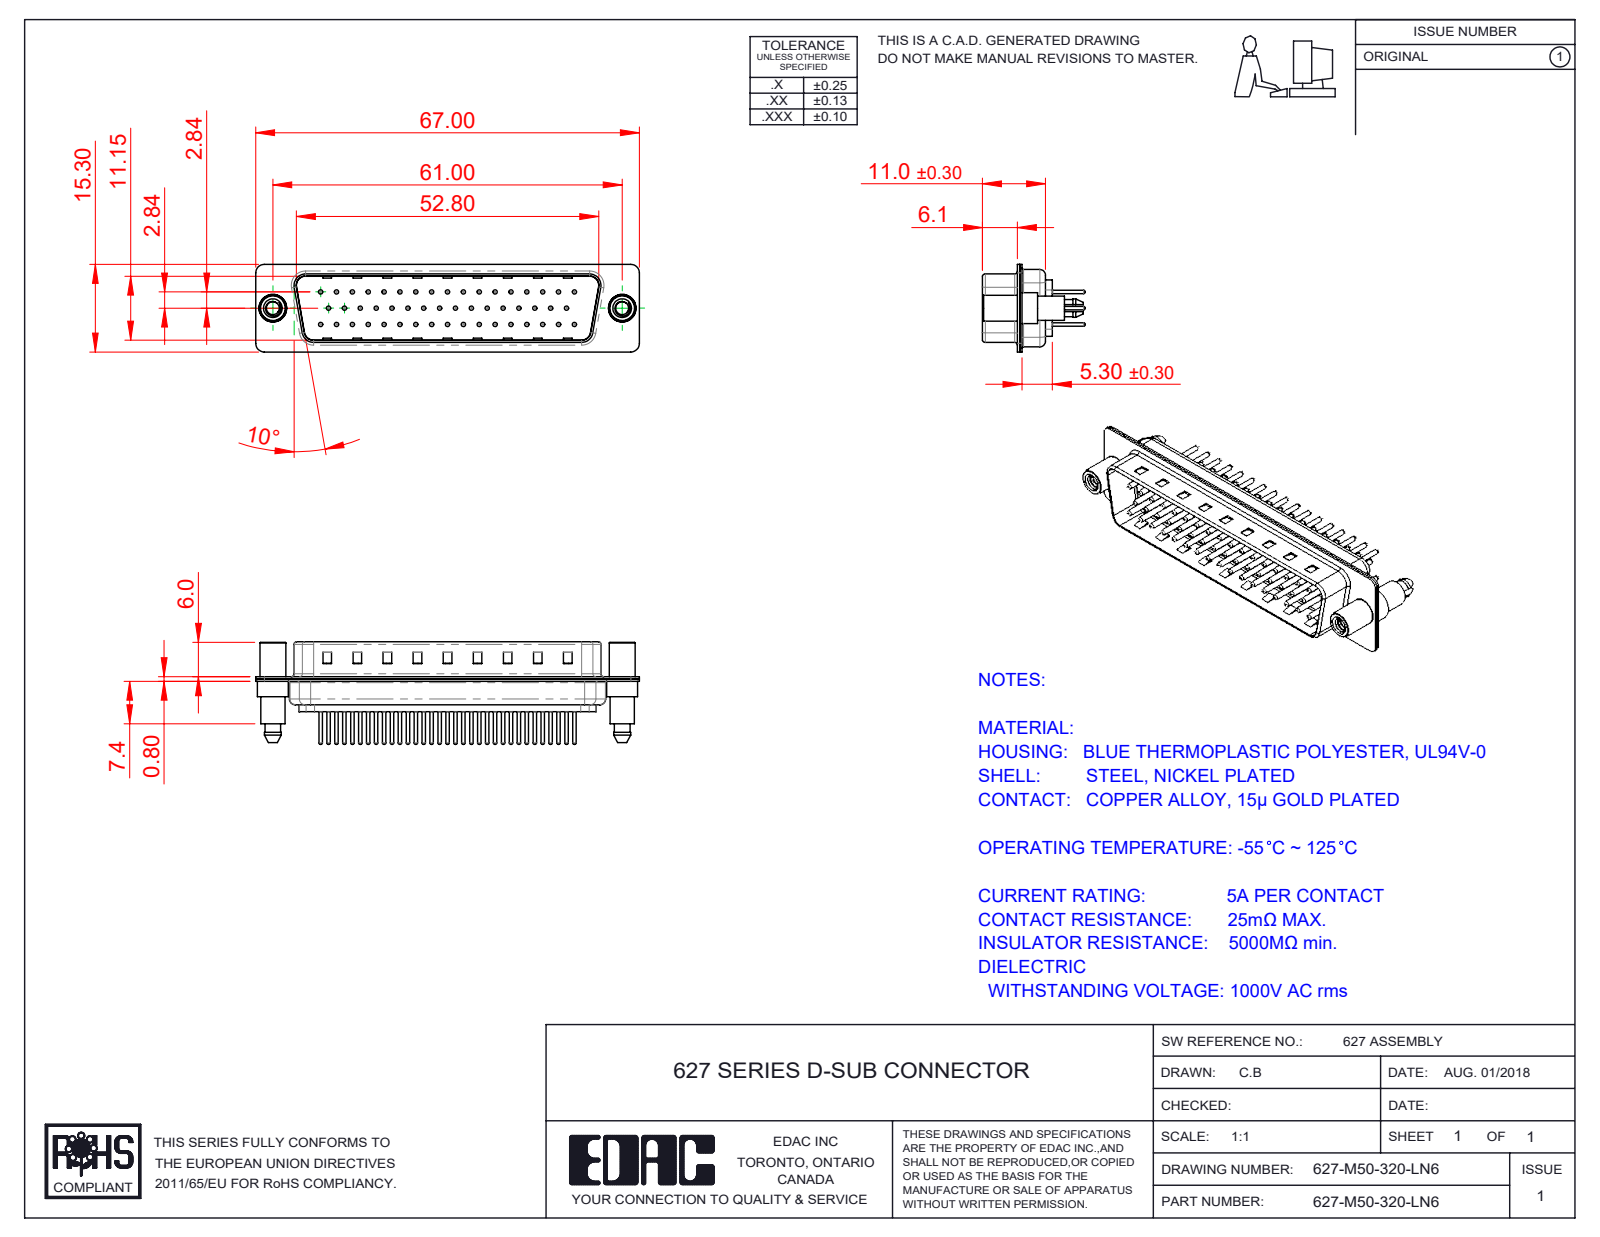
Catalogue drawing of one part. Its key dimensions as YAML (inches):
part_name: "627M Contact Row 1_20; 627-M50-320-LN6; 627M Shell Front_50 Contacts; 627M Housing_50 Contacts (+4 more)"
step_written_by: "SolidWorks 2020 (CONFIG_CONTROL_DESIGN)"
units: inches
bodies: {solids: 55, faces: 2314, planar: 571, cylindrical: 869, other: 874}
overall_size: [2.638, 0.705, 0.602]
volume: 0.297
surface_area: 17.31
round_holes:
  - {diameter: 0.03, count: 50}
  - {diameter: 0.063, count: 50}
  - {diameter: 0.079, count: 50}
  - {diameter: 0.089, count: 2}
  - {diameter: 0.157, count: 2}
  - {diameter: 0.189, count: 2}
round_bosses_or_shafts:
  - {diameter: 0.059, count: 50}
  - {diameter: 0.024, count: 50}
  - {diameter: 0.213, count: 2}
  - {diameter: 0.193, count: 2}
  - {diameter: 0.177, count: 2}
  - {diameter: 0.167, count: 2}
partial_cylinders:
  - {radius: 0.059, count: 18}
  - {radius: 0.079, count: 12}
  - {radius: 0.063, count: 10}
  - {radius: 0.02, count: 8}
  - {radius: 0.01, count: 4}
  - {radius: 0.024, count: 4}
  - {radius: 0.026, count: 4}
  - {radius: 0.035, count: 4}
face_to_face_distances: [0.016, 0.455, 0.224, 0.24, 0.031, 0.03, 0.485, 0.209, 0.485, 0.516]
hole_center_spacings: [0.124, 0.109, 0.218, 0.327, 0.436, 0.545, 0.654, 0.198]
